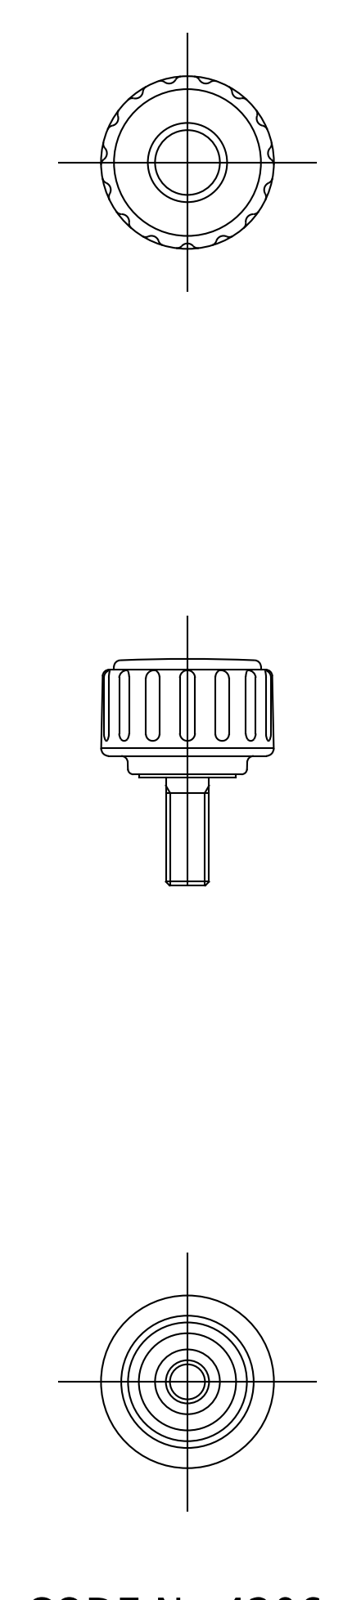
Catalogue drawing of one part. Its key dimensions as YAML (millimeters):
part_name: "screw; knob; KDM_16_M4_10_2170_36"
step_written_by: "CADfix (AUTOMOTIVE_DESIGN)"
units: millimeters
bodies: {solids: 2, faces: 68, planar: 0, cylindrical: 0, other: 68}
overall_size: [20.95, 16.12, 15.97]
volume: 1945
surface_area: 1246
